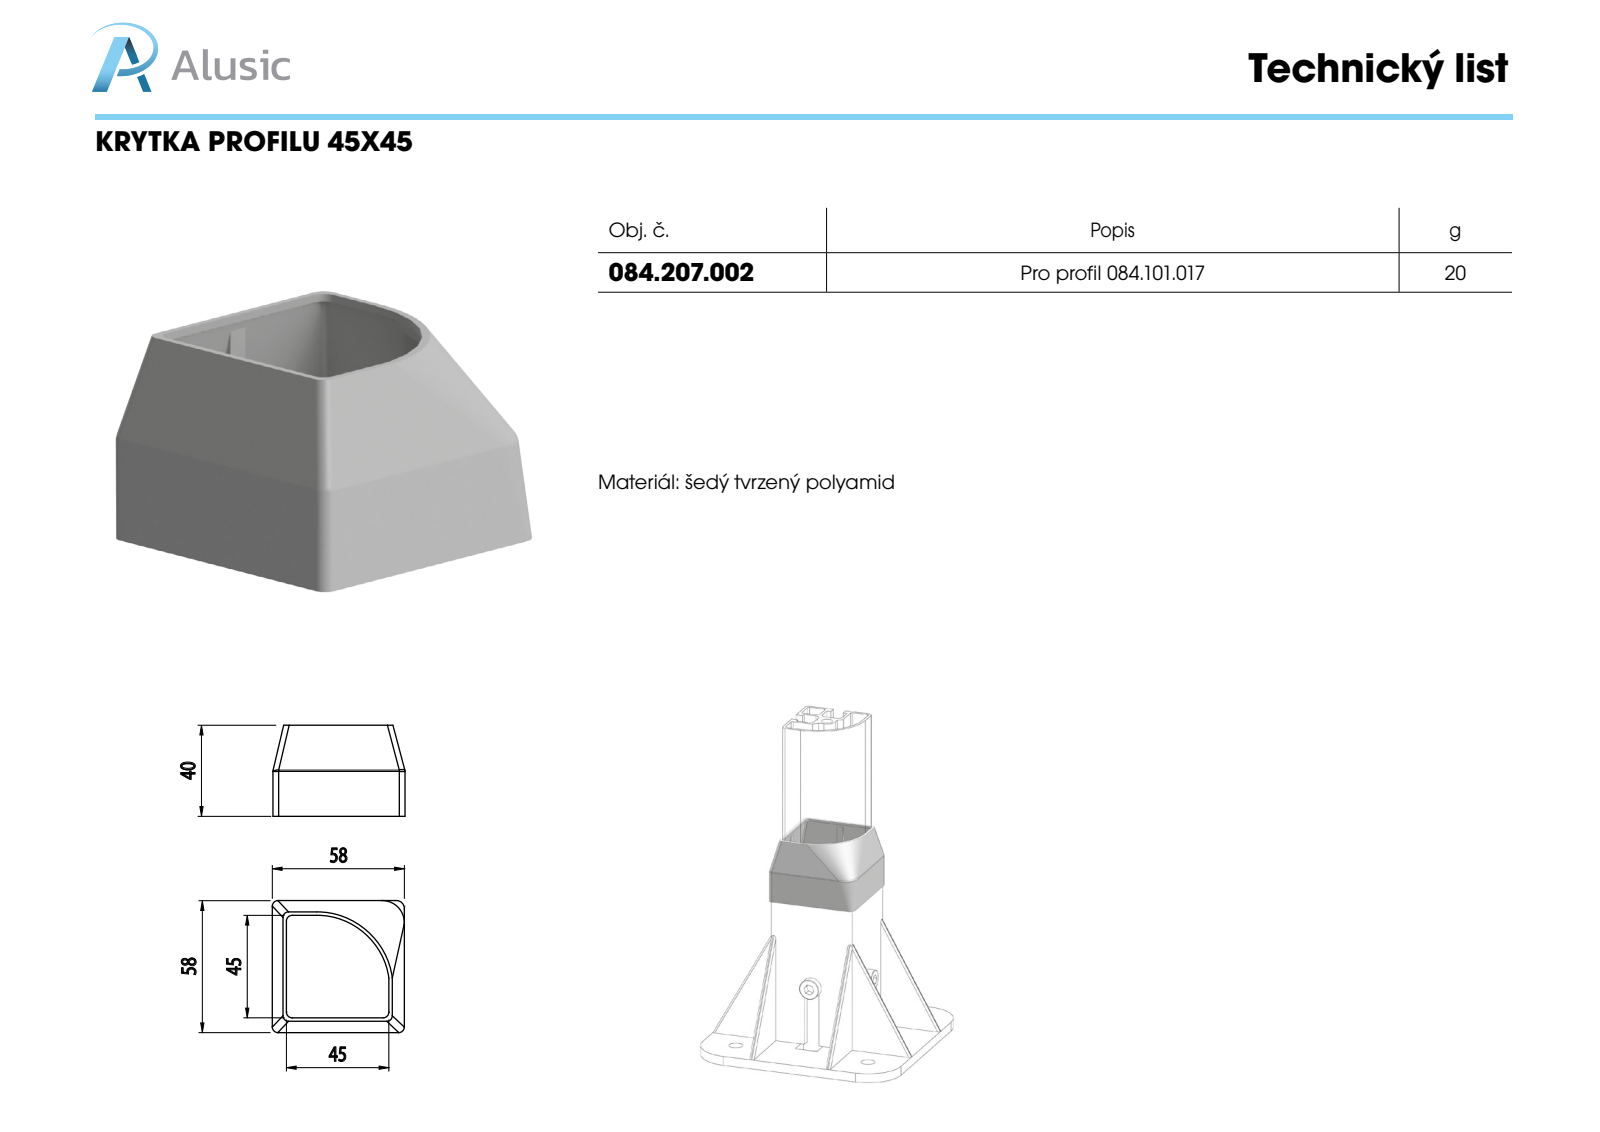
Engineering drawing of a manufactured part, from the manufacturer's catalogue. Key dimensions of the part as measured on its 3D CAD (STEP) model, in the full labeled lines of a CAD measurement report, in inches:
Part name (STEP PRODUCT): 084.207.002
STEP written by: SolidWorks 2011 (CONFIG_CONTROL_DESIGN)
Units: inches
Bodies: 1 solid, 67 faces (33 planar, 14 cylindrical, 20 other)
Overall size (bounding box): 2.283 × 2.283 × 1.575
Volume: 0.815 in³ · Surface area: 27.98 in²
Partial cylindrical surfaces — rounded edges, fillets, slot ends (radius × count): R0.098 ×10, R0.039 ×3, R1.26 ×1
Main face-to-face distances: 0.059, 1.004, 1.575, 0.157, 0.846, 0.217, 0.787, 1.063, 1.22, 1.161
